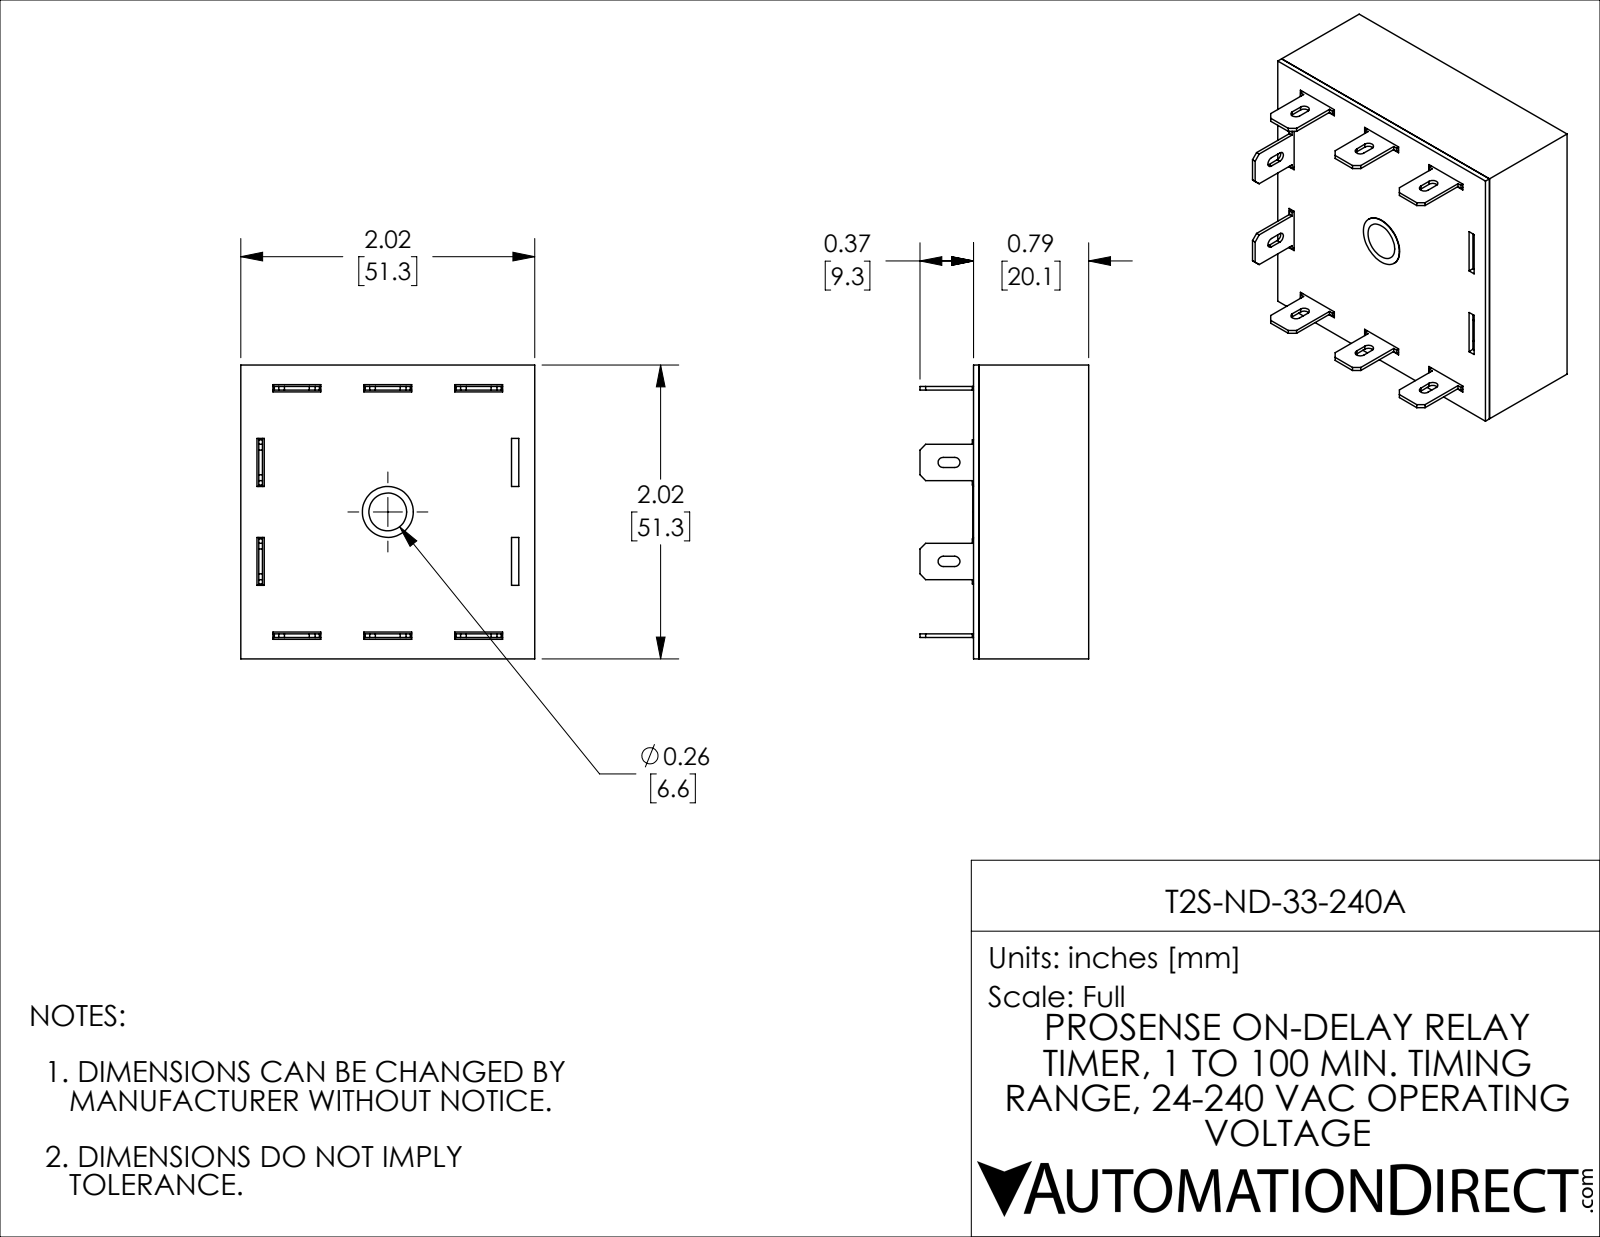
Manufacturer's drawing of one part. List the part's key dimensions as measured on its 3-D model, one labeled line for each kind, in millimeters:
Part name (STEP PRODUCT): T2S-ND-33-240A
STEP written by: SolidWorks 2021 (CONFIG_CONTROL_DESIGN)
Units: millimetres
Bodies: 10 solids, 256 faces (234 planar, 20 cylindrical, 2 other)
Overall size (bounding box): 51.31 × 51.31 × 29.46
Volume: 11 042 mm³ · Surface area: 22 819 mm²
Round holes (diameter × count): ⌀8.89 ×1
Partial cylindrical surfaces — rounded edges, fillets, slot ends (radius × count): R0.89 ×10
Main face-to-face distances: 1.14, 50.16, 19.15, 20.12, 0.97, 18.01, 18.98, 51.3, 49.02, 3.74
